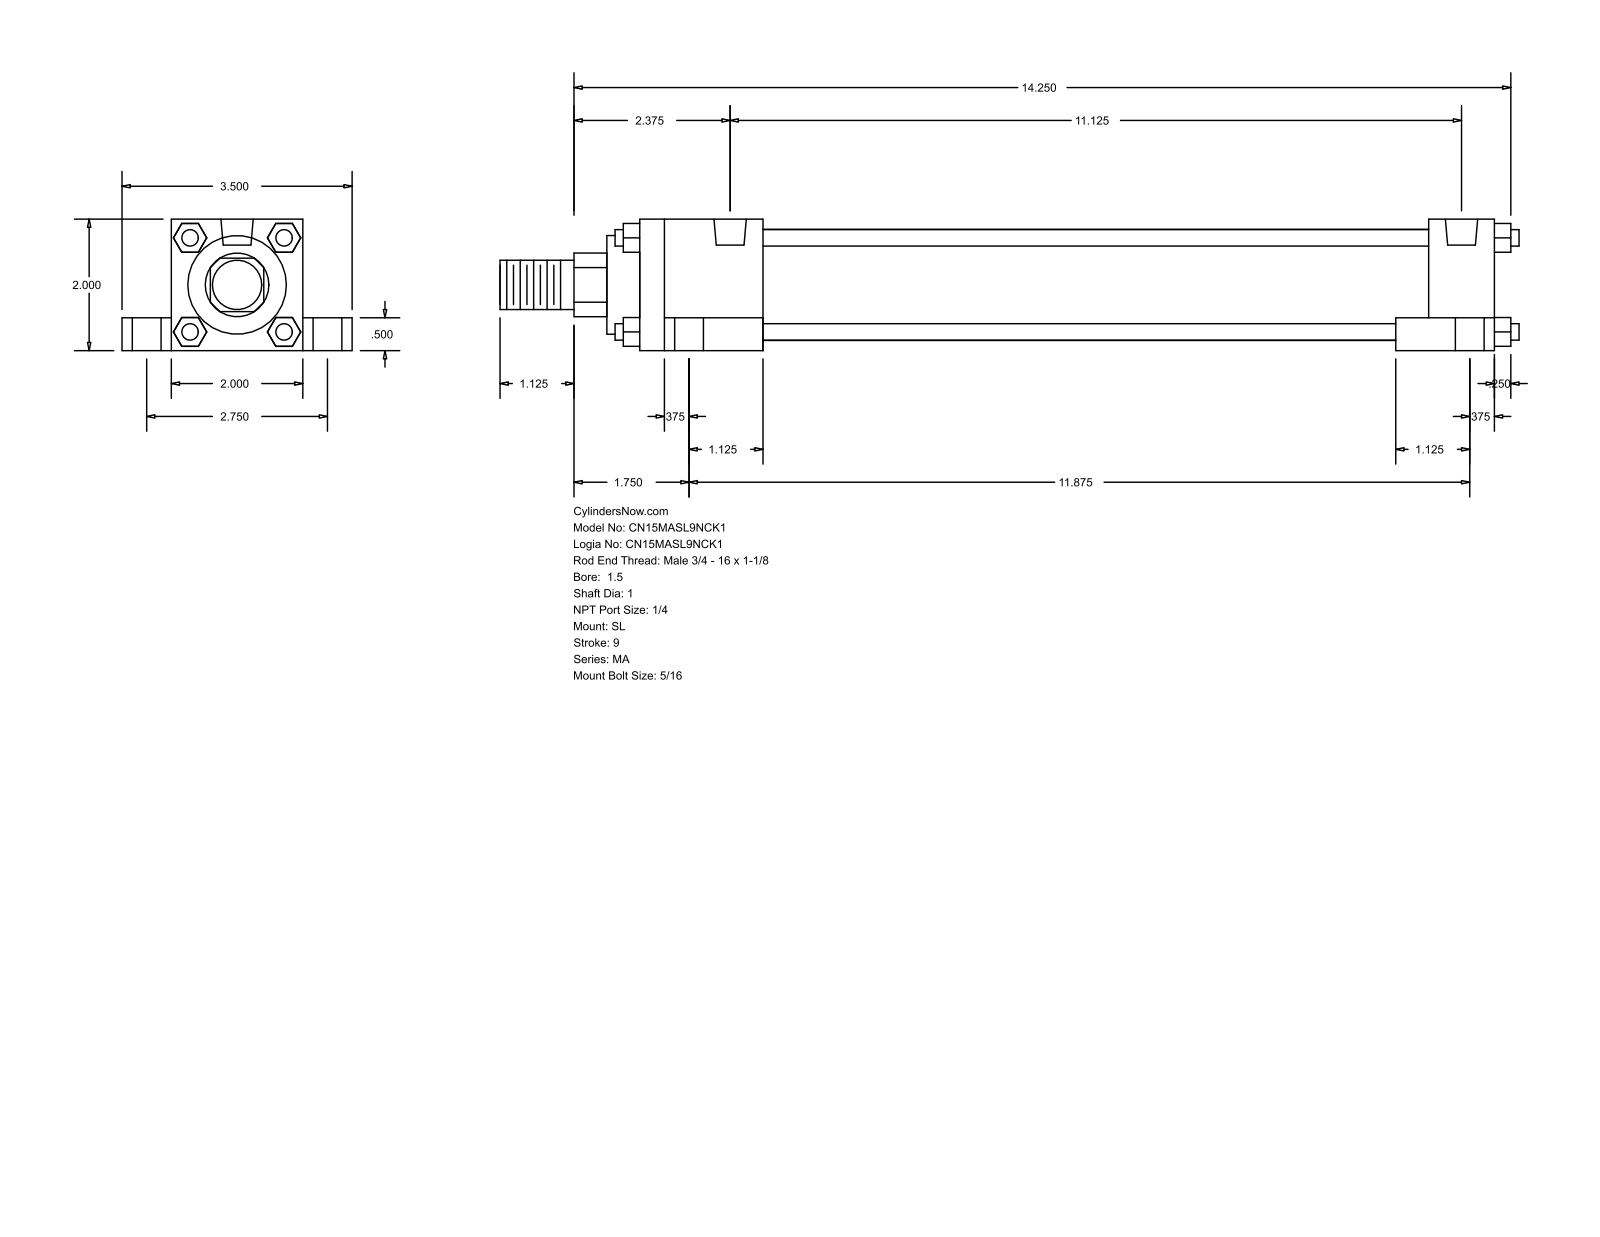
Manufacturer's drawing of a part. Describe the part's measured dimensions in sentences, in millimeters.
The part is named "MA_SL__0150_1". Its 3-D file was written by "GSSL Pune (CONFIG_CONTROL_DESIGN)". It is 0 solids with 148 faces: 112 planar, 36 cylindrical and 0 other. Overall it measures 393.7 by 88.9 by 50.8 millimeters. Round holes: 4 of diameter 7.94, 4 of diameter 11.11, 4 of diameter 17.46, 2 of diameter 12.49. Round bosses or shafts: 4 of diameter 6.35, 1 of diameter 42.93, 1 of diameter 38.1, 1 of diameter 25.4, 1 of diameter 19.05. Partial cylindrical surfaces (rounded edges, fillets, slot ends): 1 of radius 12.29. The main face-to-face distances are 50.8, 12.7, 19.05, 69.85, 38.1, 9.52, 330.2, 25.4, 6.35, 304.8. The hole center spacings are 35.06, 38.36, 69.84, 282.57, 287.87, 300.49, 301.62, 309.6.
